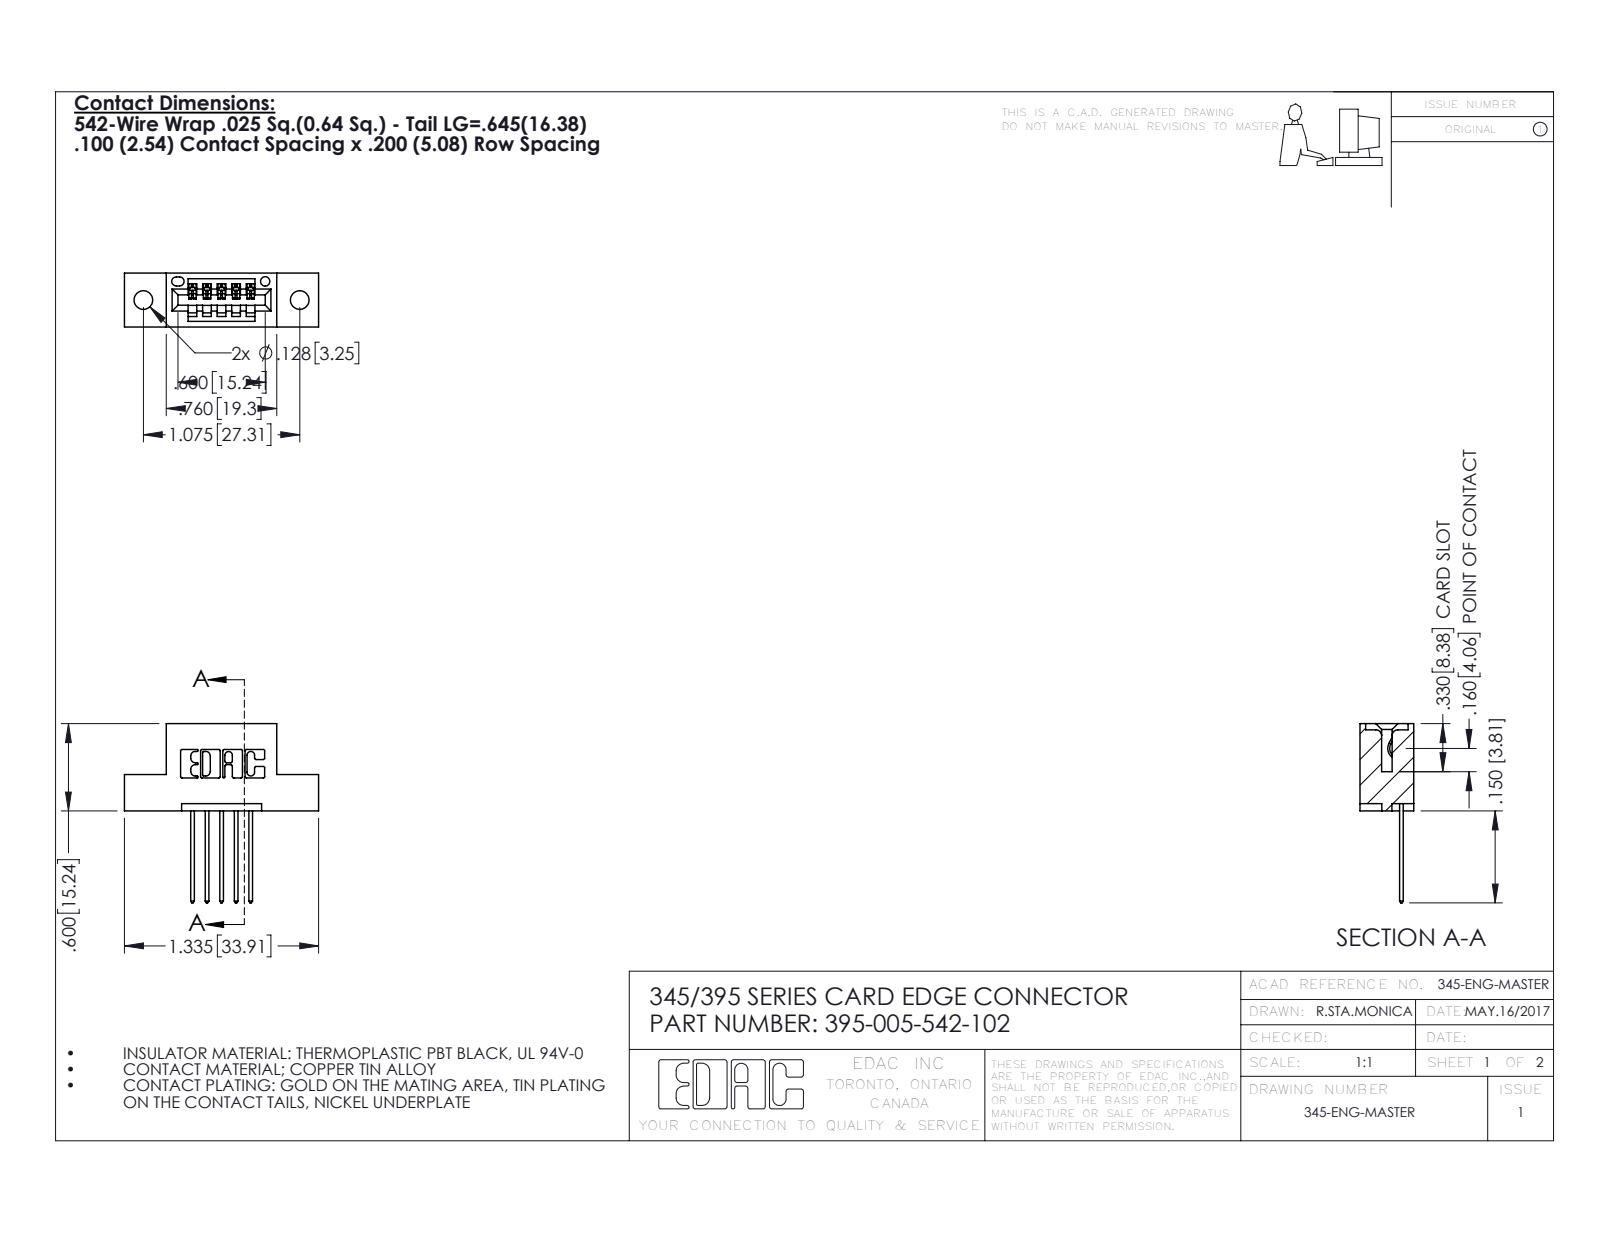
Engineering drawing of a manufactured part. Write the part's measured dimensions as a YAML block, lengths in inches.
part_name: "345-292-001_345-293-142; 345 Part_Flush Mounting Lugs - 0.128 Dia; 395-005-542-102"
step_written_by: "SolidWorks 2016 (CONFIG_CONTROL_DESIGN)"
units: inches
bodies: {solids: 6, faces: 416, planar: 280, cylindrical: 136, other: 0}
overall_size: [1.335, 1.232, 0.37]
volume: 0.176
surface_area: 4.866
round_holes:
  - {diameter: 0.128, count: 2}
  - {diameter: 0.064, count: 1}
partial_cylinders:
  - {radius: 0.01, count: 22}
  - {radius: 0.006, count: 10}
  - {radius: 0.01, count: 10}
  - {radius: 0.007, count: 6}
  - {radius: 0.031, count: 6}
  - {radius: 0.026, count: 3}
  - {radius: 0.031, count: 2}
  - {radius: 0.04, count: 2}
face_to_face_distances: [0.2, 0.37, 0.298, 0.072, 0.1, 0.098, 0.272, 0.025, 0.25, 0.06]
hole_center_spacings: [0.27, 0.847, 1.075]
